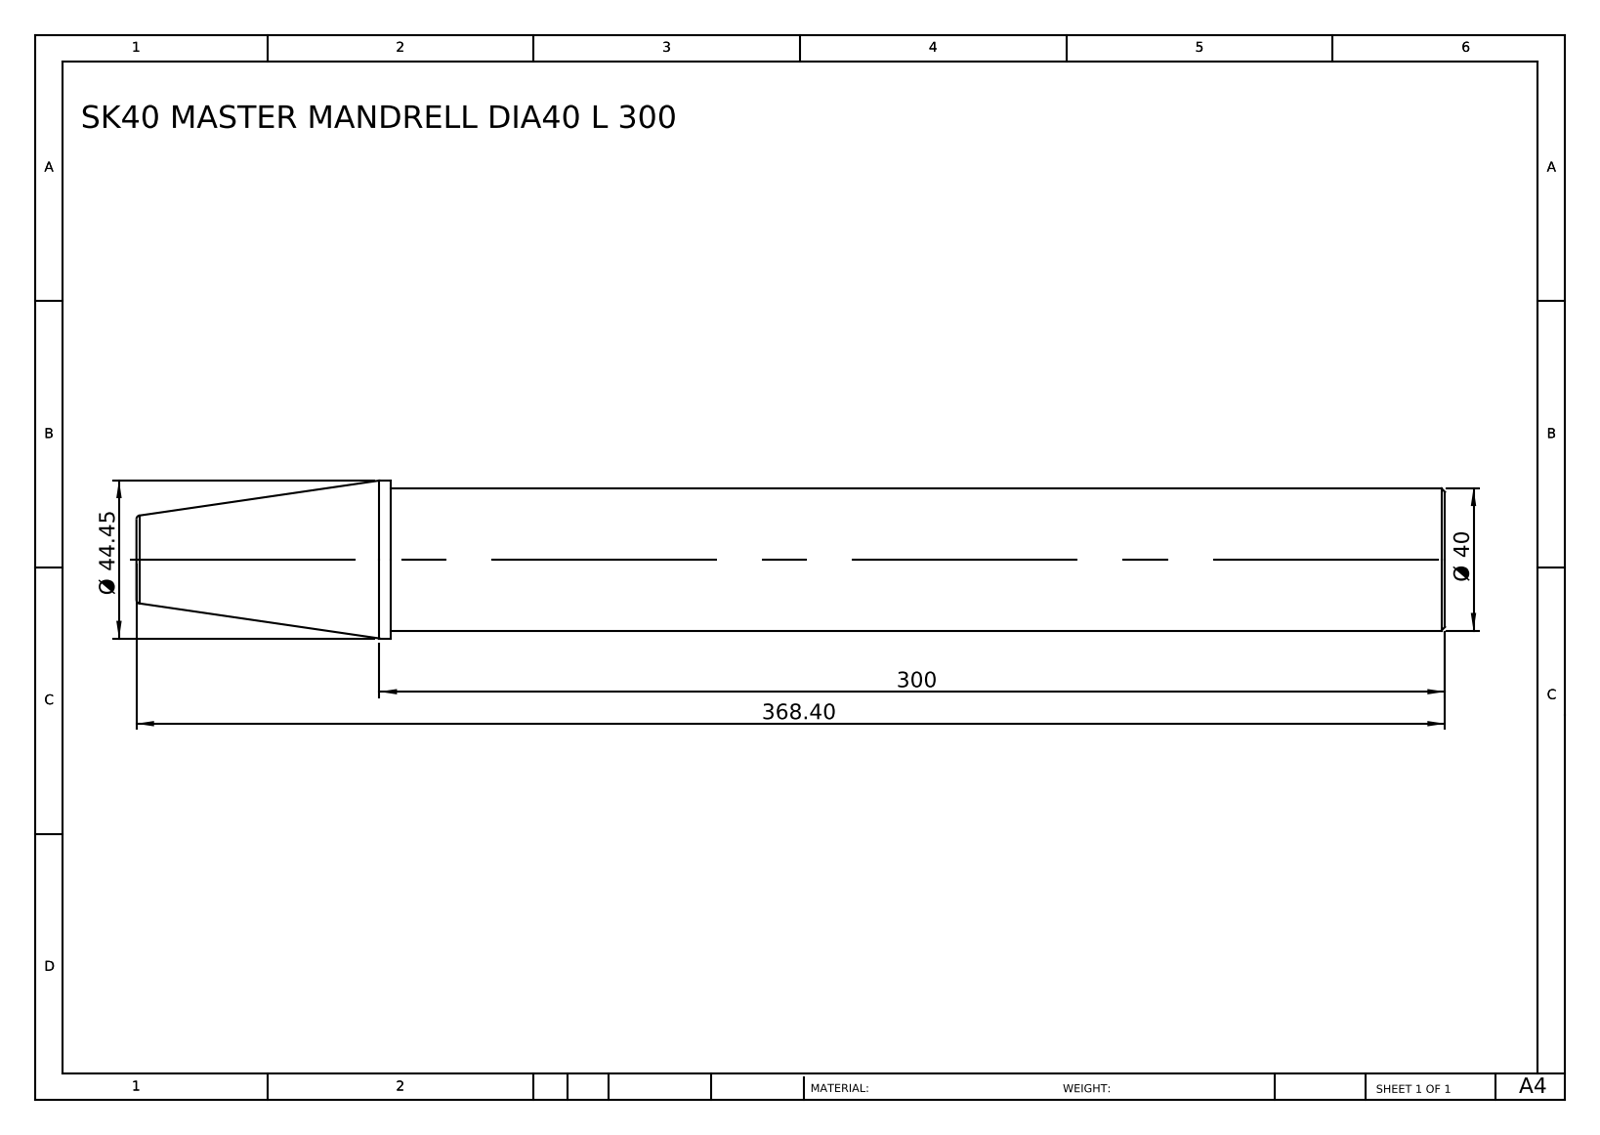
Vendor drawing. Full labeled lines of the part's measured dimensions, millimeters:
Part name (STEP PRODUCT): SK40 MASTER MANDRELL DIA40 L300
STEP written by: SolidWorks 2014 (CONFIG_CONTROL_DESIGN)
Units: millimetres
Bodies: 1 solid, 13 faces (3 planar, 4 cylindrical, 6 other)
Overall size (bounding box): 368.4 × 44.45 × 44.45
Volume: 443 496 mm³ · Surface area: 47 155 mm²
Round bosses / shafts (diameter × count): ⌀44.45 ×1, ⌀40 ×1
Main face-to-face distances: 368.4, 296.8, 71.6
